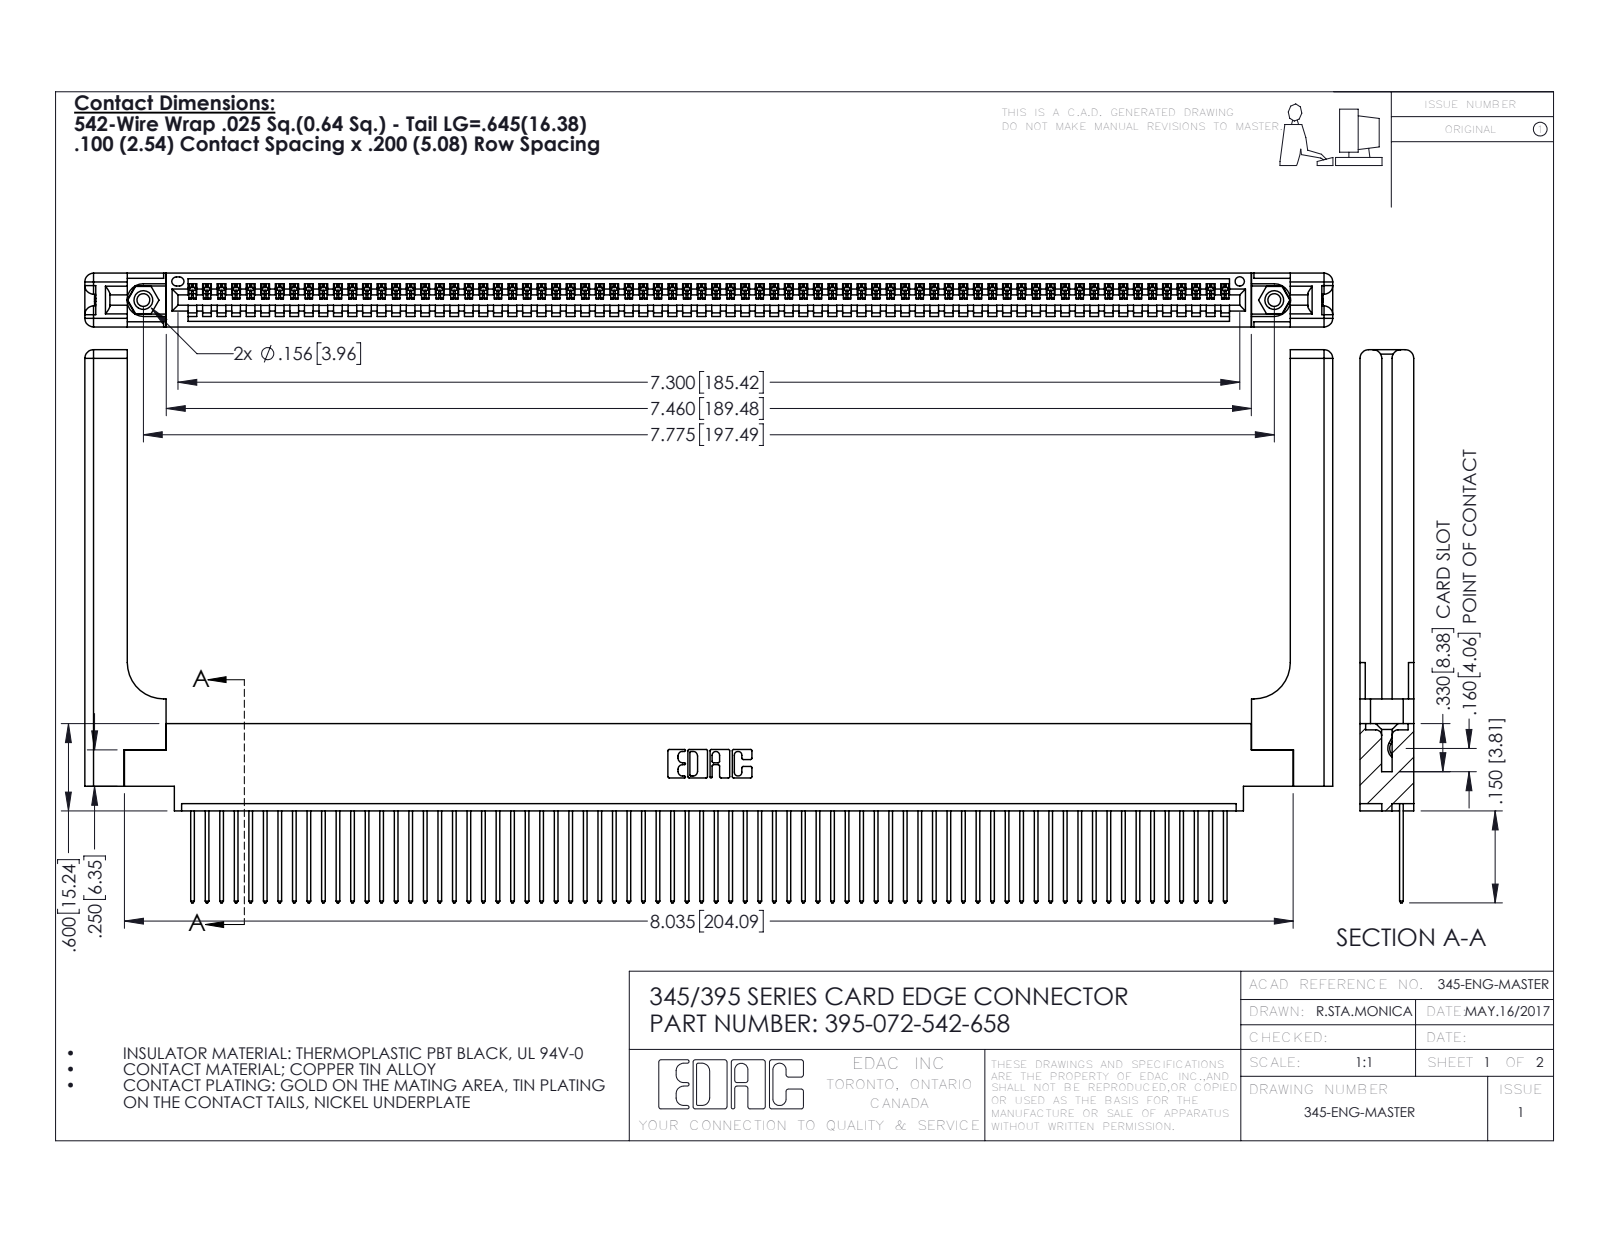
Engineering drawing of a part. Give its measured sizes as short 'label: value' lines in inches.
name: 395-072-542-658; 345-292-001_345-293-142; 345-220-058_345-220-058; 345 Part_0.170 Offset - 0.156 Dia-TH (+1 more)
written by: SolidWorks 2016 (CONFIG_CONTROL_DESIGN)
unit: in
bodies: 77 solids, 4562 faces (3112 planar, 1390 cylindrical, 60 other)
size: 8.579 × 3.802 × 0.37
volume: 1.8 in³; area: 53.86 in²
holes: 2× ⌀0.089, 2× ⌀0.125, 2× ⌀0.156, 1× ⌀0.064
bosses: 2× ⌀0.155
rounds: 144× R0.006, 144× R0.01, 22× R0.01, 16× R0.06, 6× R0.007, 6× R0.031, 3× R0.026, 2× R0.03
face distances: 0.072, 0.298, 0.37, 0.098, 0.272, 0.025, 0.2, 0.225, 0.148, 0.15
hole spacings: 0.27, 7.539, 7.775
